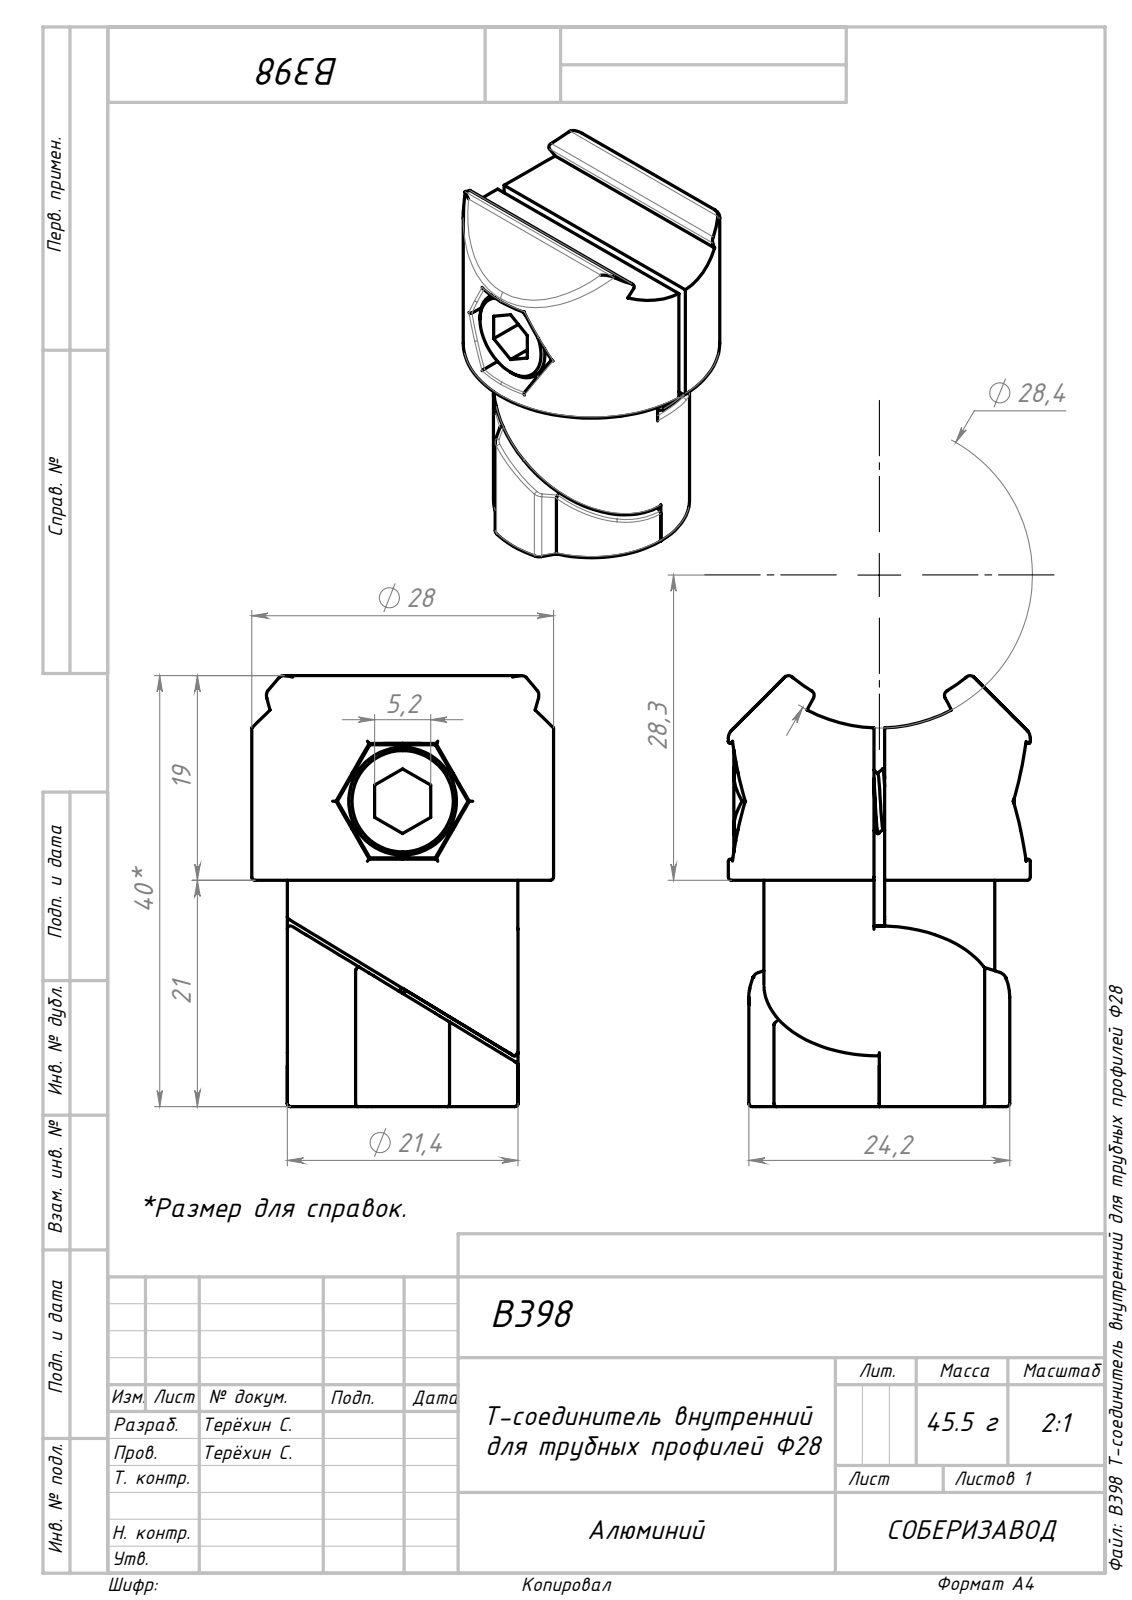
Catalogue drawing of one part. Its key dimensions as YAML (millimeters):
part_name: "B398 Т-соединитель внутренний для трубных профилей Ф28.stp"
step_written_by: "SolidWorks 2022 (AUTOMOTIVE_DESIGN)"
units: millimeters
bodies: {solids: 4, faces: 299, planar: 76, cylindrical: 104, other: 119}
overall_size: [40, 28, 27.98]
volume: 15687
surface_area: 8810
round_holes:
  - {diameter: 5.2, count: 1}
  - {diameter: 6.5, count: 1}
round_bosses_or_shafts:
  - {diameter: 28, count: 1}
  - {diameter: 21.4, count: 1}
  - {diameter: 10, count: 1}
  - {diameter: 6, count: 1}
partial_cylinders:
  - {radius: 0.5, count: 20}
  - {radius: 0.3, count: 8}
  - {radius: 1, count: 4}
  - {radius: 12, count: 1}
  - {radius: 12.1, count: 1}
  - {radius: 12.45, count: 1}
  - {radius: 14.2, count: 1}
face_to_face_distances: [0.5, 1, 0.4, 7, 6.5, 6, 10.28, 21, 13, 10]
